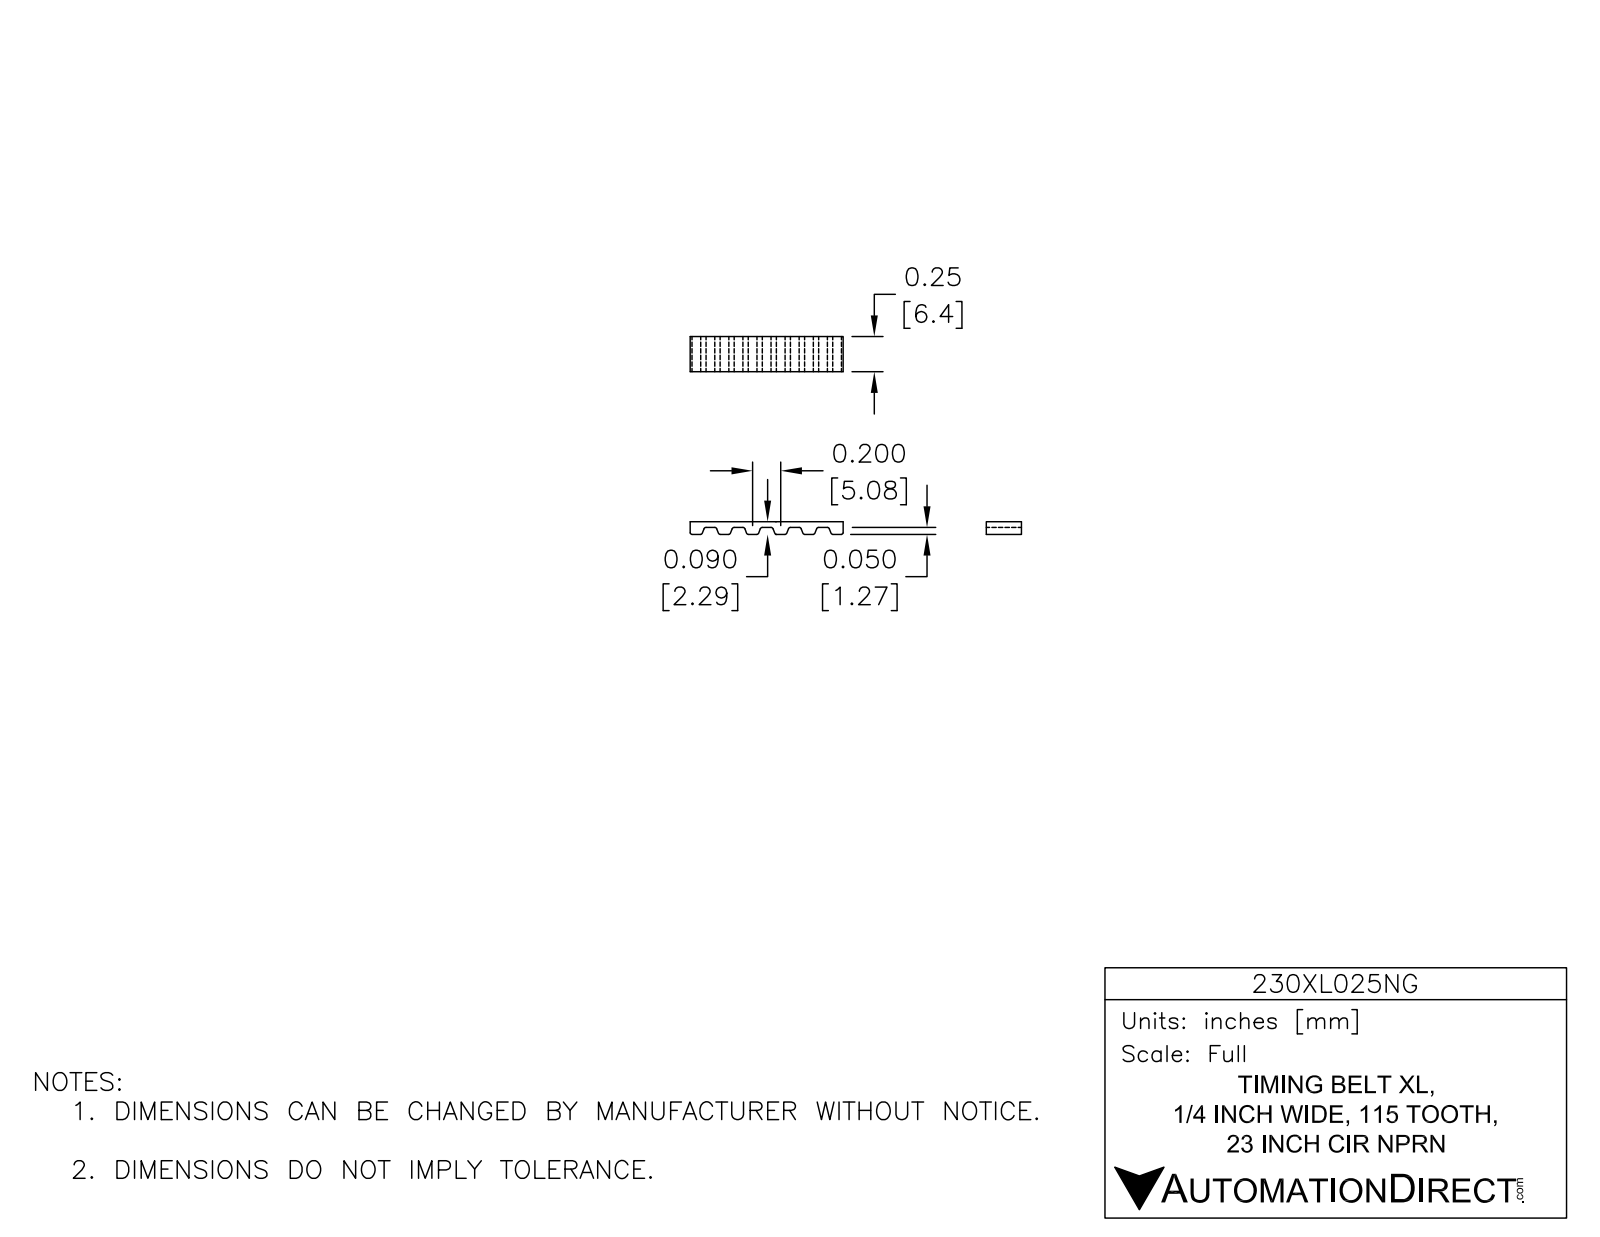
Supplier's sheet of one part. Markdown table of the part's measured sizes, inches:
| quantity | value |
| --- | --- |
| part name | 230XL025NG |
| STEP written by | SolidWorks 2014 (AUTOMOTIVE_DESIGN) |
| units | inches |
| bodies | 1 solid, 960 faces (418 planar, 542 cylindrical, 0 other) |
| overall size | 9.788 × 3 × 0.25 |
| volume | 0.313 in³ |
| surface area | 15.53 in² |
| partial cylindrical surfaces (radius × count) | 0.015 × 460, 1.46 × 2, 1.5 × 2 |
| main face-to-face distances | 3, 0.04, 2.96, 0.25, 2.92, 0.09, 2.91, 0.05, 2.87, 0.179 |
